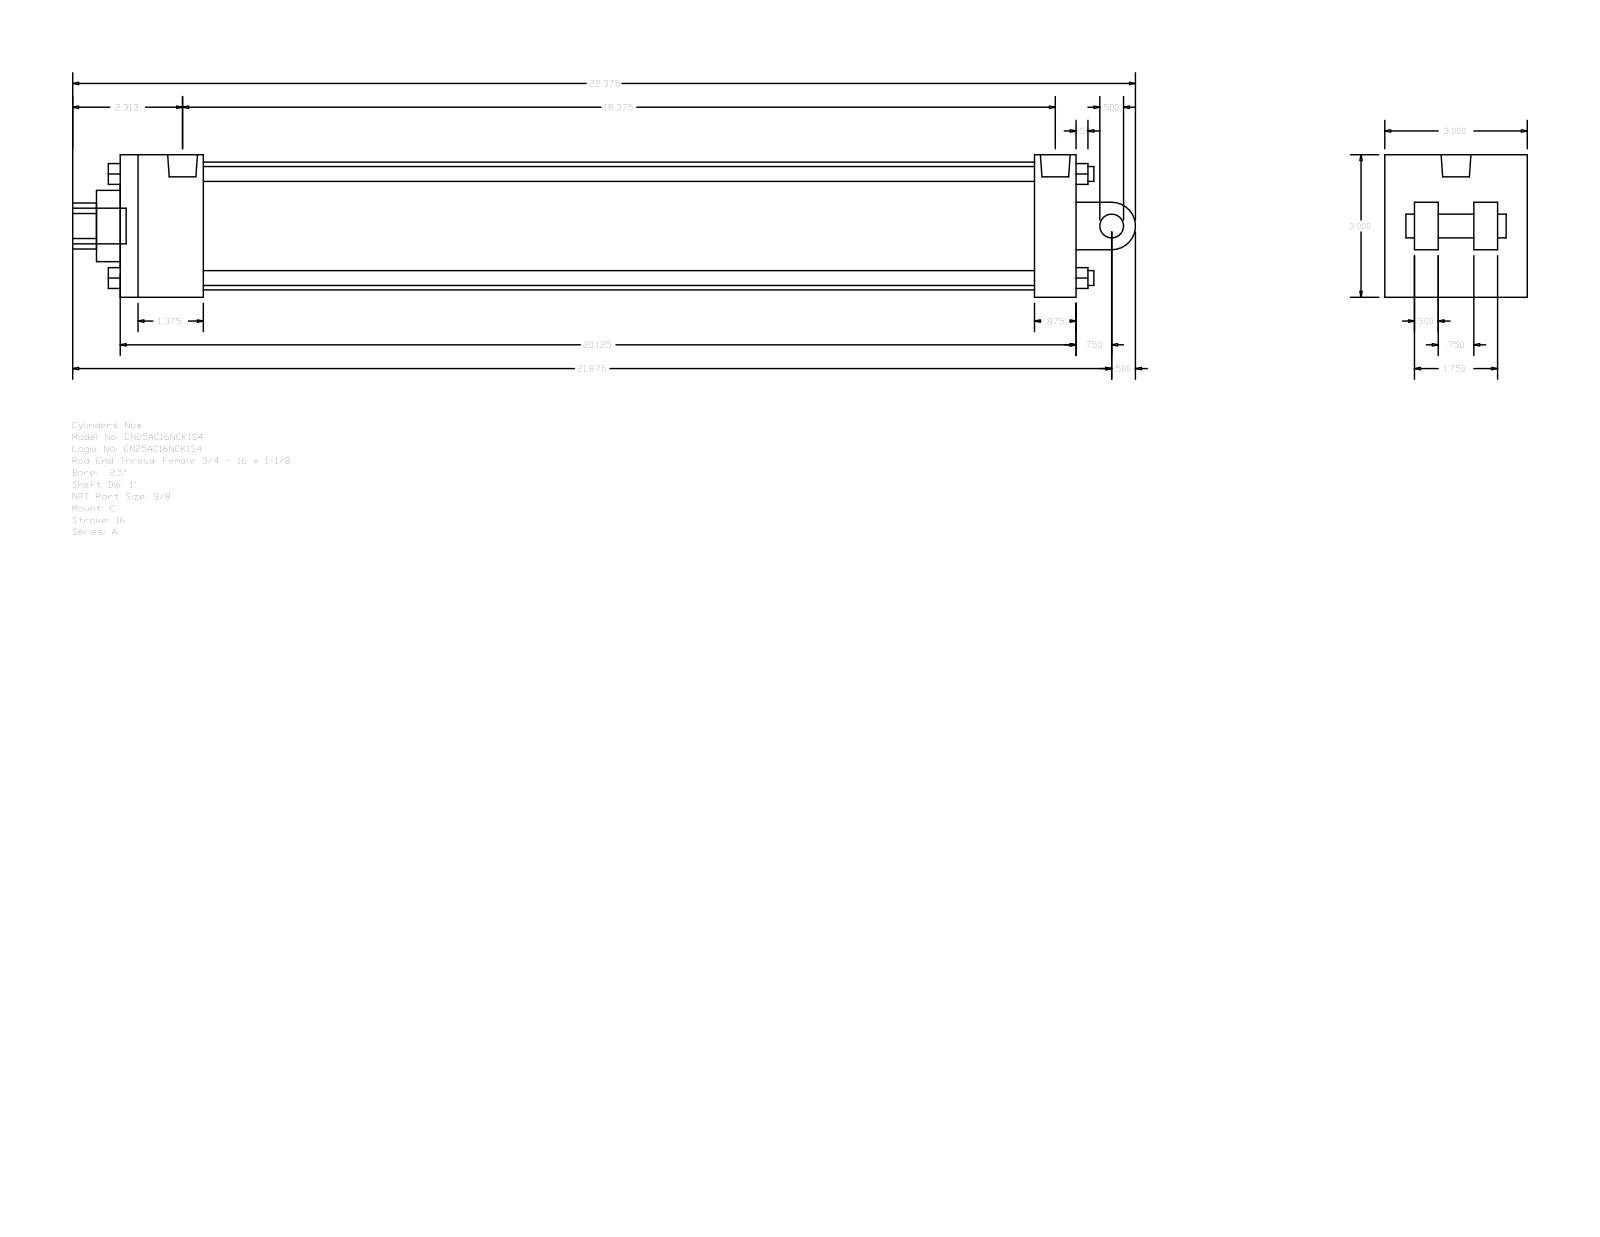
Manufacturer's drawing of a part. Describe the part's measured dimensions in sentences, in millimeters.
The part is named "A_C__0250_1". Its 3-D file was written by "GSSL Pune (CONFIG_CONTROL_DESIGN)". It is 0 solids with 135 faces: 102 planar, 33 cylindrical and 0 other. Overall it measures 568.33 by 76.2 by 76.2 millimeters. Round holes: 2 of diameter 5.56, 1 of diameter 15.93, 1 of diameter 25.4, 1 of diameter 38.1, 1 of diameter 68.33. Round bosses or shafts: 4 of diameter 7.94, 2 of diameter 5.56, 1 of diameter 19.05, 1 of diameter 15.93, 1 of diameter 12.7. Partial cylindrical surfaces (rounded edges, fillets, slot ends): 1 of radius 12.29, 1 of radius 12.7. The main face-to-face distances are 76.2, 511.18, 12.7, 44.45, 488.95, 444.5, 466.73, 22.23, 15.87, 25.4. The hole center spacings are 2.38.
